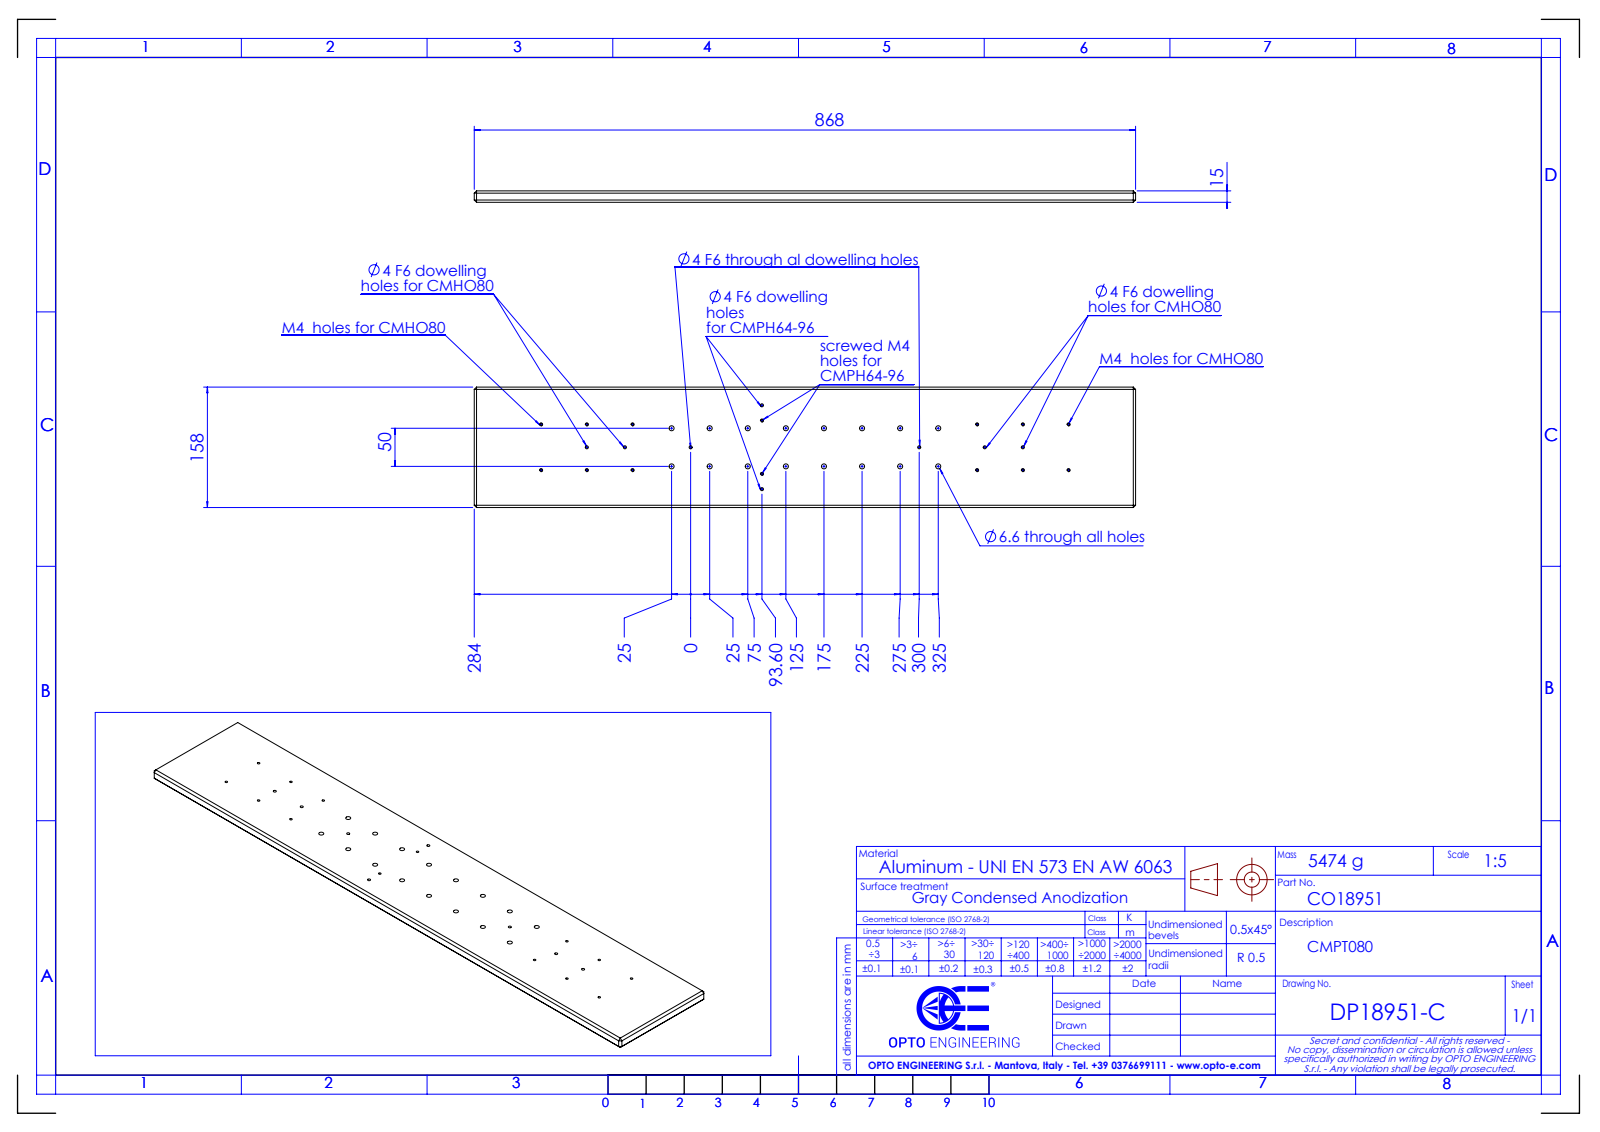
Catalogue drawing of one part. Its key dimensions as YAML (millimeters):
part_name: "DP18951-C_CMPT080"
step_written_by: "SolidWorks 2021 (AUTOMOTIVE_DESIGN)"
units: millimeters
bodies: {solids: 1, faces: 108, planar: 32, cylindrical: 76, other: 0}
overall_size: [868, 158, 15]
volume: 2028000
surface_area: 304510
round_holes:
  - {diameter: 6.6, count: 16}
  - {diameter: 3.3, count: 14}
  - {diameter: 4, count: 8}
face_to_face_distances: [15, 158, 118.07, 868, 620.04, 620.03, 721.14, 10, 5, 593.73]
hole_center_spacings: [50, 70.71, 100, 111.8, 150, 158.11, 35.36, 200]
